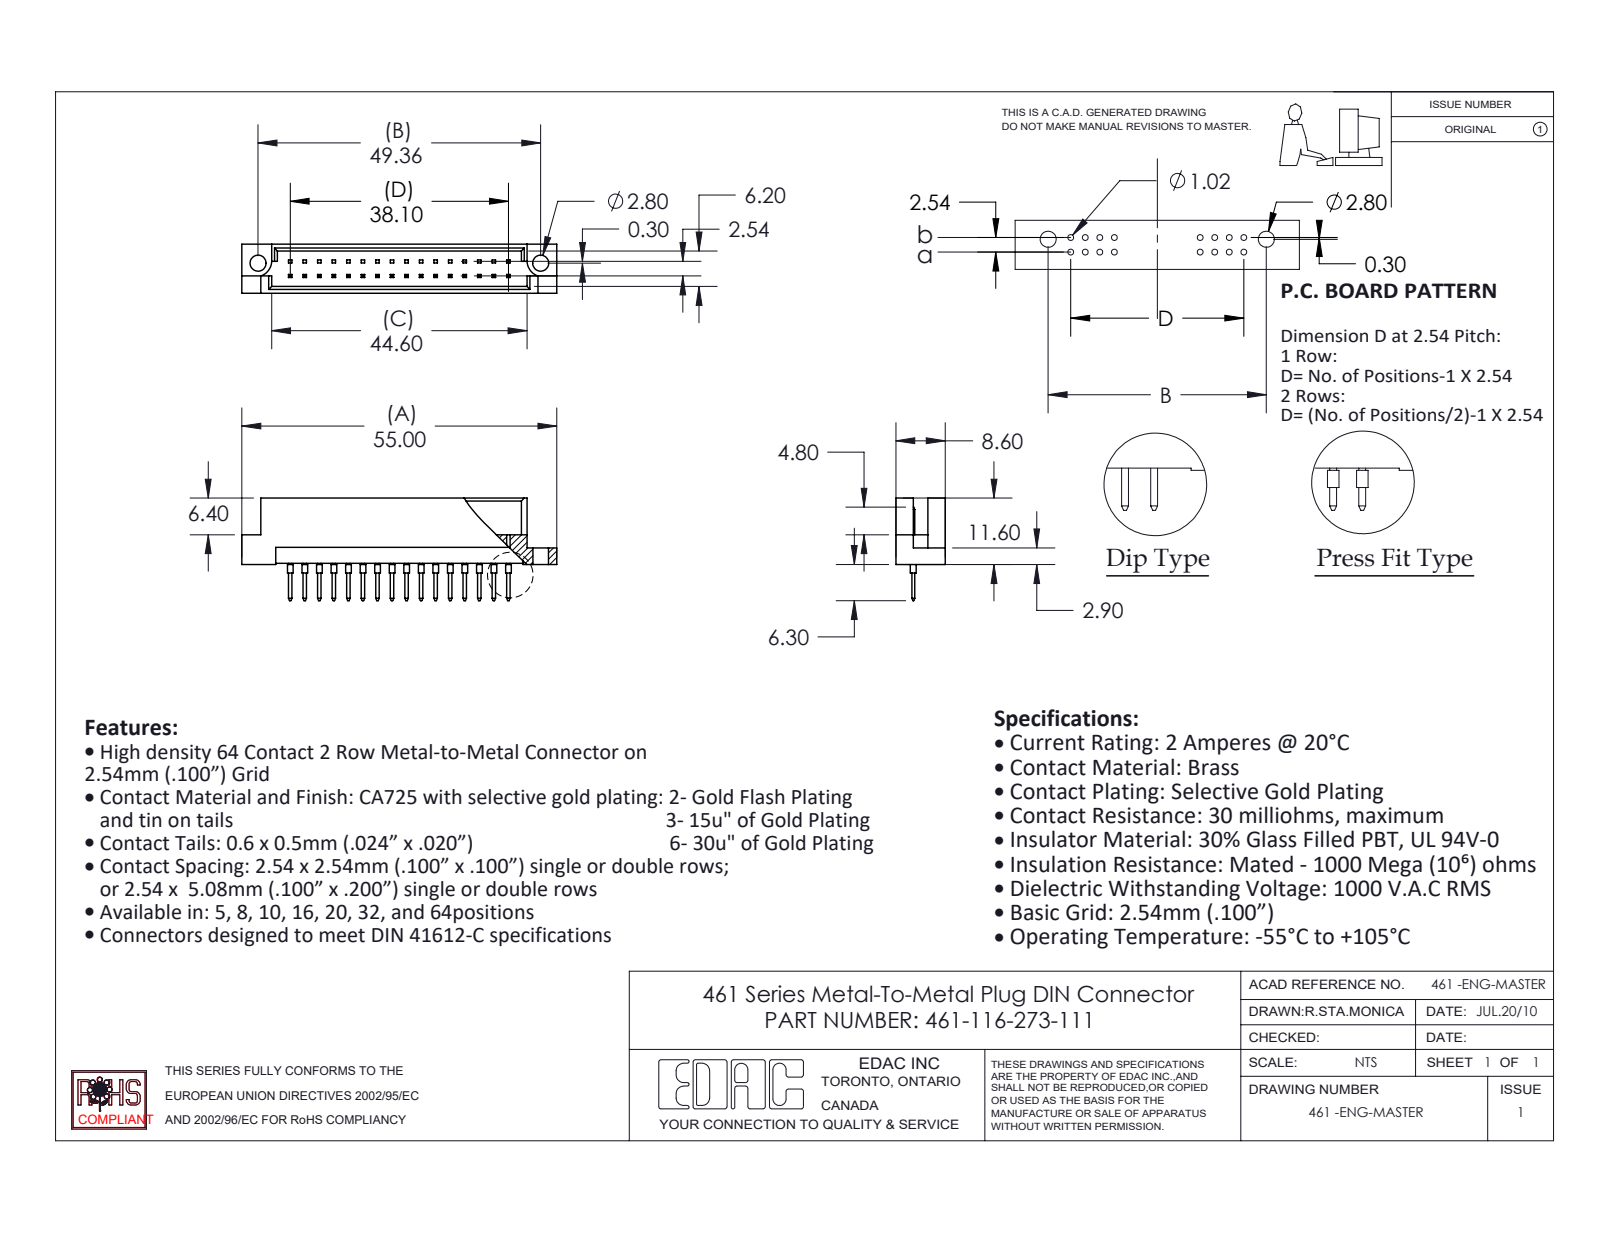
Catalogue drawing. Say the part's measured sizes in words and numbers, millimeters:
The part is named "461-290_73; 461 Part_32; 461-116-273-111". Its 3-D file was written by "SolidWorks 2020 (CONFIG_CONTROL_DESIGN)". It is 17 solids with 528 faces: 490 planar, 38 cylindrical and 0 other. Overall it measures 55 by 17.9 by 8.6 millimeters. Its volume is 2 742 cubic millimeters and its surface area 3 854 square millimeters. Round holes: 2 of diameter 2.8. Round bosses or shafts: 16 of diameter 1. Partial cylindrical surfaces (rounded edges, fillets, slot ends): 2 of radius 2.8. The main face-to-face distances are 1.2, 7.4, 8.6, 6.2, 2.54, 5, 2.78, 5.82, 1.58, 4.62. The hole center spacings are 49.36.
